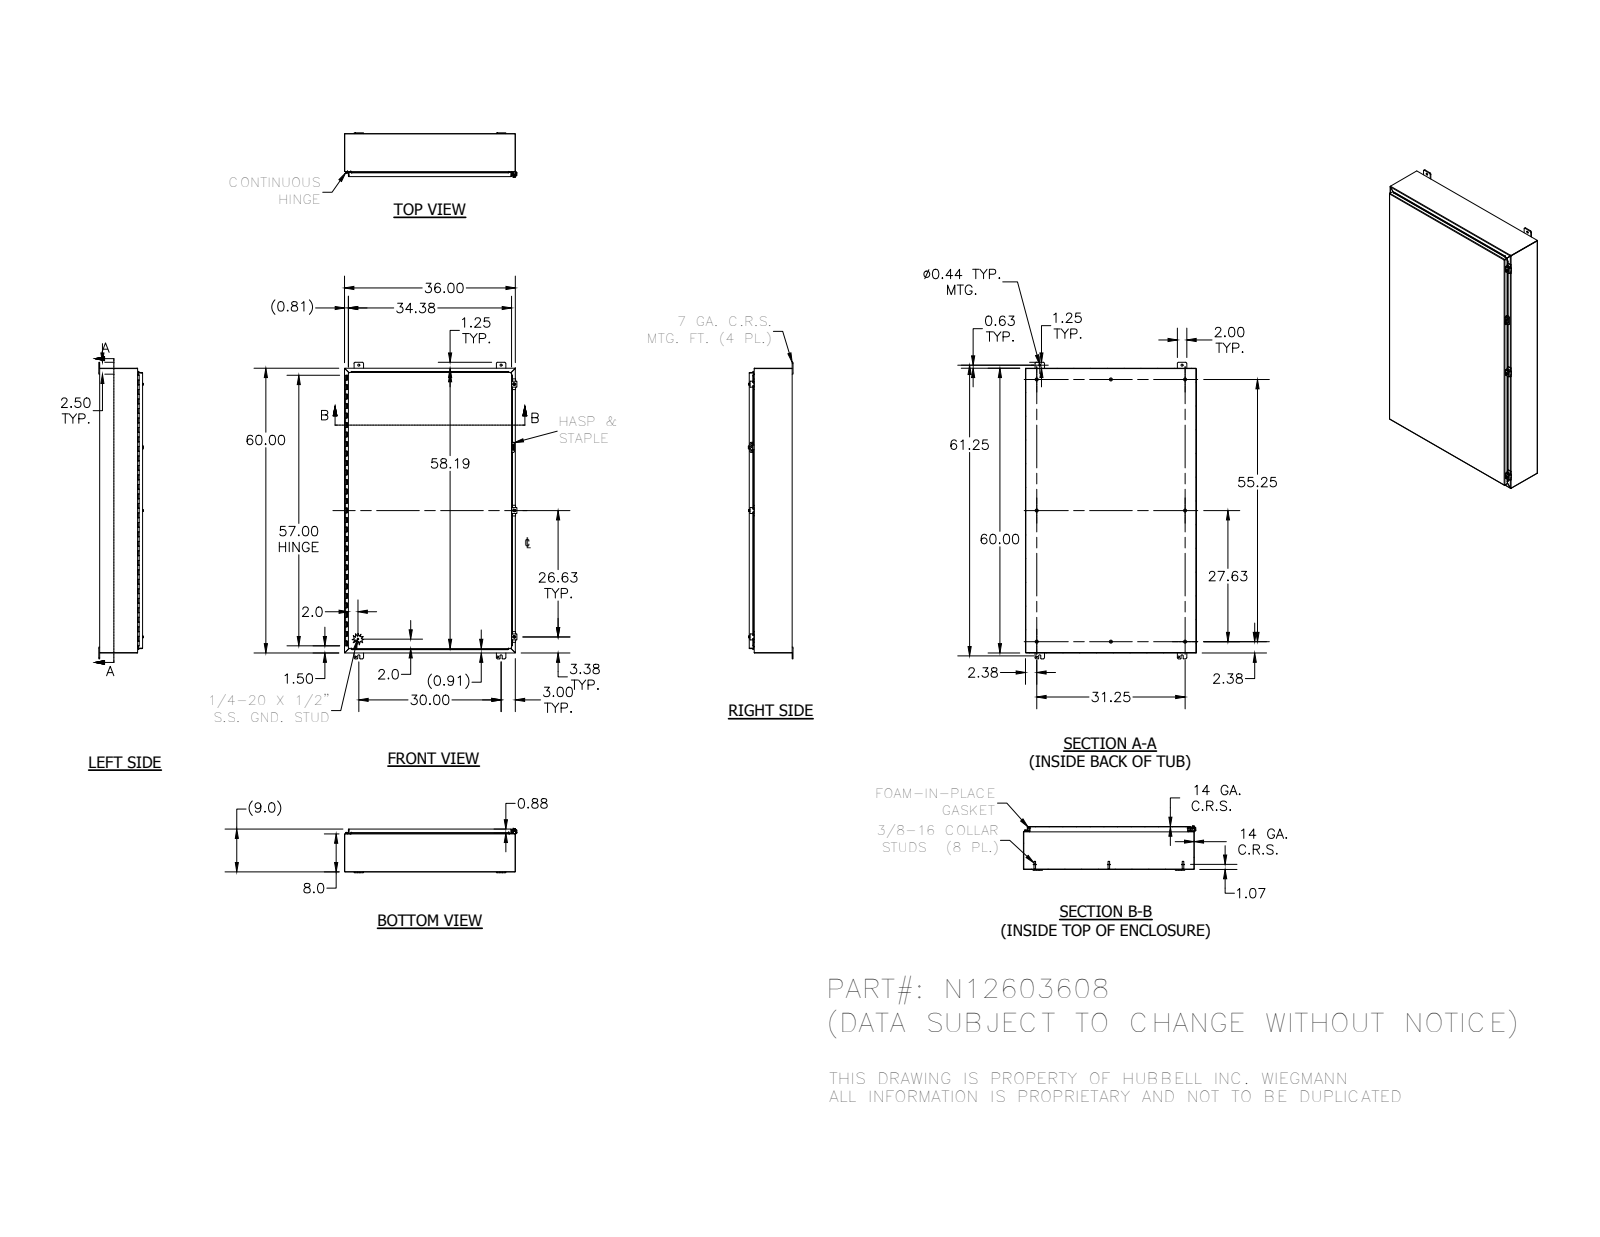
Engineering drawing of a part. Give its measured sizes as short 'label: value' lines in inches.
name: N12603608; 34840; 38413; N123608TB (+8 more)
written by: Autodesk Inventor 2012 (AUTOMOTIVE_DESIGN)
unit: in
bodies: 38 solids, 1357 faces (806 planar, 428 cylindrical, 123 other)
size: 62.5 × 36.311 × 9.41
volume: 496.6 in³; area: 13 158 in²
holes: 4× ⌀0.313, 4× ⌀0.438, 3× ⌀0.11, 3× ⌀0.211, 3× ⌀0.281, 3× ⌀0.3, 1× ⌀0.125, 1× ⌀0.156, 1× ⌀0.5
bosses: 8× ⌀0.625, 8× ⌀0.33, 5× ⌀0.25, 3× ⌀0.52, 3× ⌀0.5, 3× ⌀0.35, 1× ⌀0.337, 1× ⌀0.12
rounds: 39× R0.03, 27× R0.125, 27× R0.25, 21× R0.031, 21× R0.105, 15× R0.063, 6× R0.1, 6× R0.141
face distances: 0.074, 8.959, 8.885, 9.033, 35.926, 59.926, 7.926, 1.033, 36, 35.852
hole spacings: 1.593, 30, 60, 67.082, 0.791, 13.327, 29.348, 30.72
